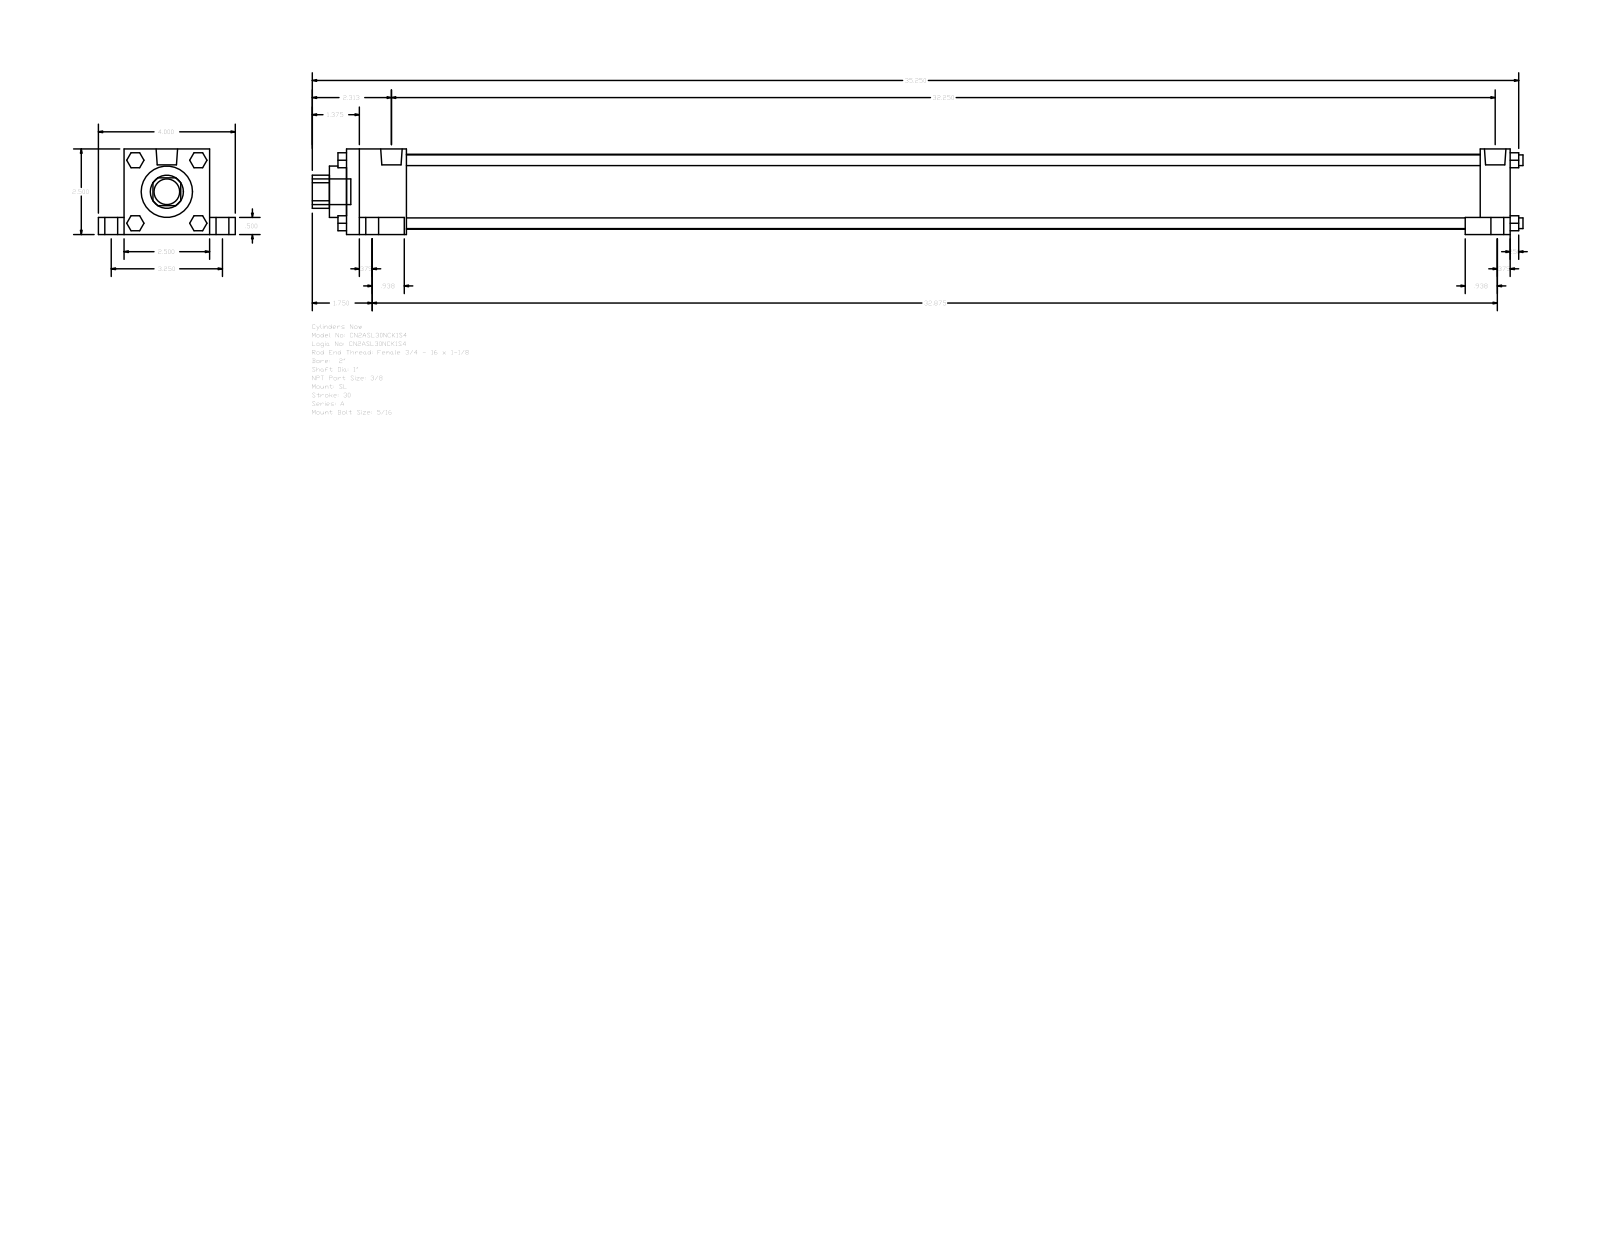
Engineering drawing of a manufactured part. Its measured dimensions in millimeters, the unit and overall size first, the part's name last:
Units: millimetres
Overall size (bounding box): 898.52 × 101.6 × 63.5
Round holes (diameter × count): ⌀25.4 ×1, ⌀38.1 ×1, ⌀55.63 ×1
Round bosses / shafts (diameter × count): ⌀15.88 ×4, ⌀9.53 ×4, ⌀7.94 ×4, ⌀5.56 ×4, ⌀15.93 ×2, ⌀19.05 ×1
Partial cylindrical surfaces — rounded edges, fillets, slot ends (radius × count): R12.29 ×1
Main face-to-face distances: 63.5, 863.6, 12.7, 50.8, 19.05, 82.55, 9.52, 44.45, 819.15, 841.37
Bodies: 0 solids, 148 faces (112 planar, 36 cylindrical, 0 other)
Part name (STEP PRODUCT): A_SL__0200_1
STEP written by: GSSL Pune (CONFIG_CONTROL_DESIGN)
